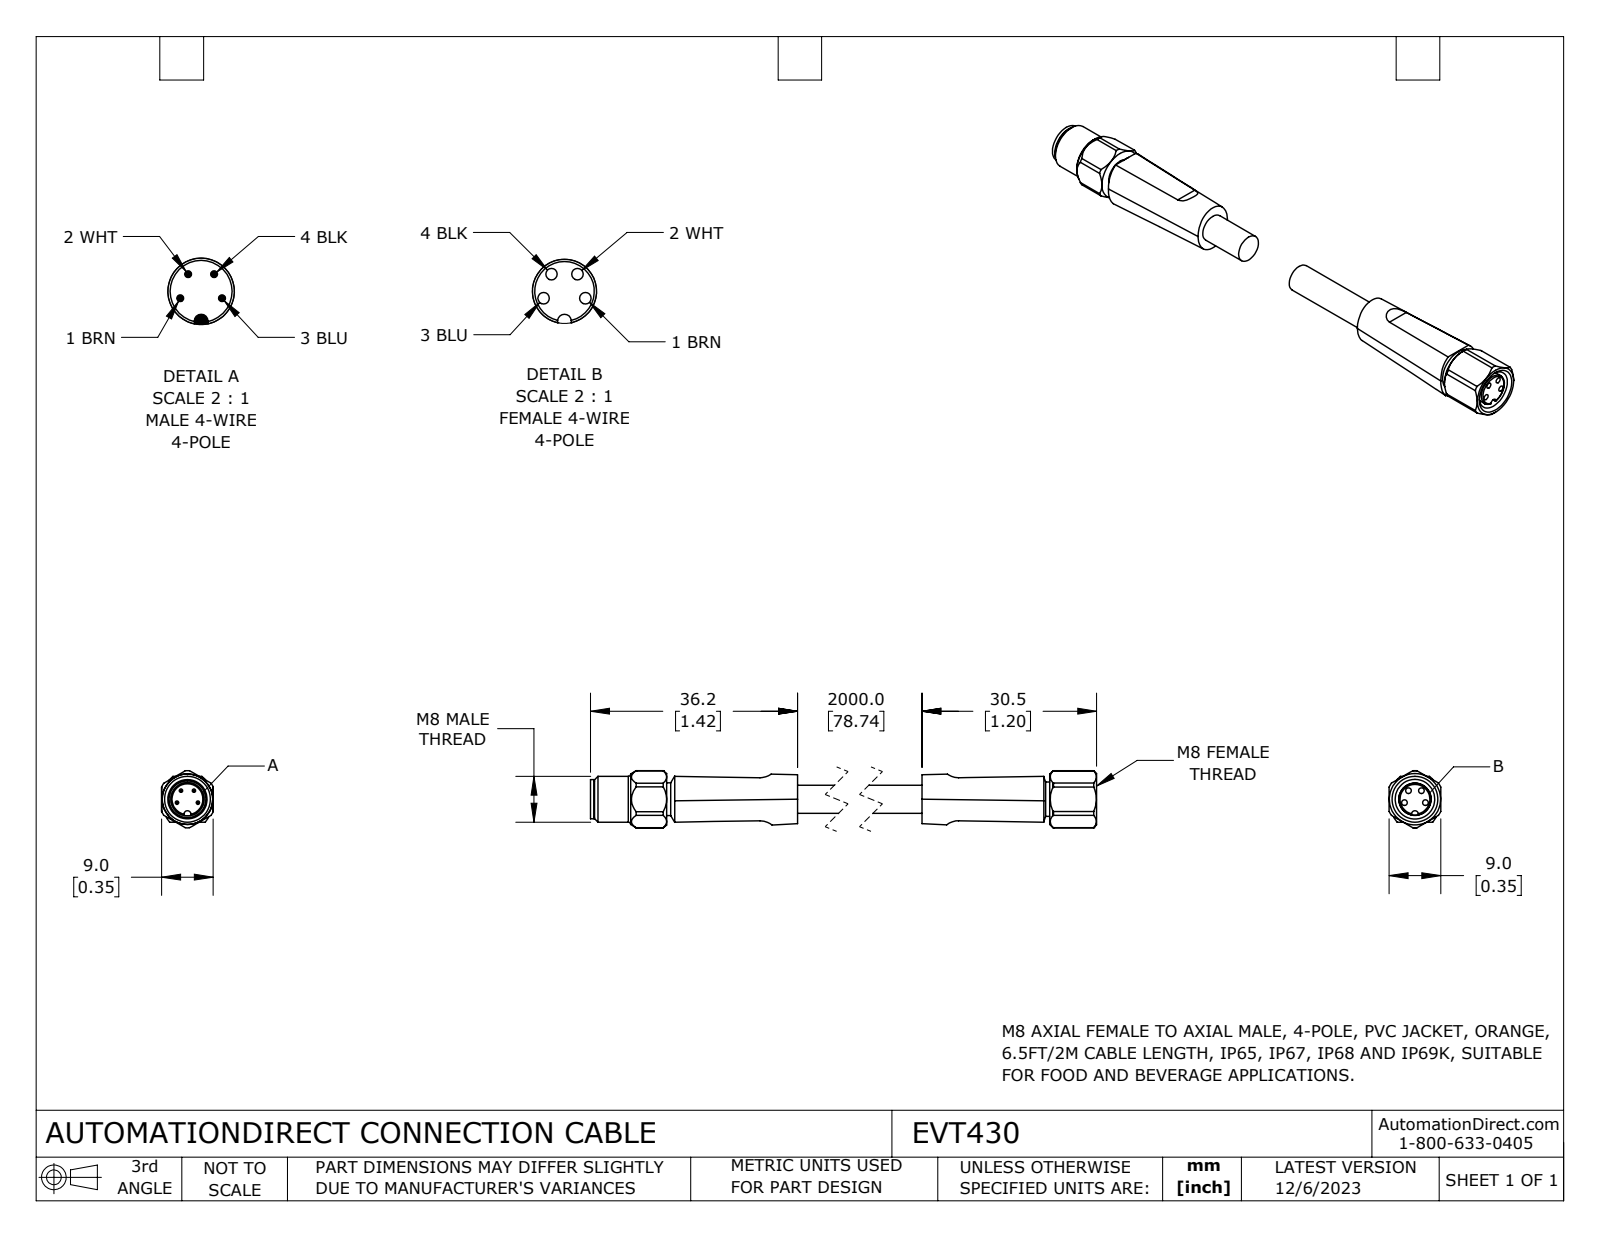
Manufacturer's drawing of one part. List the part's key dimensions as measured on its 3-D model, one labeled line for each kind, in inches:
Part name (STEP PRODUCT): EVT430_MALE; EVT430; EVT430_FEMALE
STEP written by: SolidWorks 2023 (CONFIG_CONTROL_DESIGN)
Units: inches
Bodies: 2 solids, 150 faces (47 planar, 58 cylindrical, 45 other)
Overall size (bounding box): 4.173 × 0.393 × 0.354
Volume: 0.244 in³ · Surface area: 4.751 in²
Round holes (diameter × count): ⌀0.039 ×4, ⌀0.228 ×1, ⌀0.272 ×1
Round bosses / shafts (diameter × count): ⌀0.023 ×4, ⌀0.315 ×1, ⌀0.27 ×1, ⌀0.248 ×1, ⌀0.236 ×1, ⌀0.224 ×1, ⌀0.222 ×1, ⌀0.193 ×1
Partial cylindrical surfaces — rounded edges, fillets, slot ends (radius × count): R0.133 ×4, R0.024 ×1, R0.196 ×1, R0.196 ×1
Main face-to-face distances: 0.354, 0.26, 0.26, 0.354, 3.327, 1.201, 2.449, 0.878, 0.9, 1.549
Hole centre spacings: 0.074, 0.076, 0.087, 0.143, 0.089, 0.143
